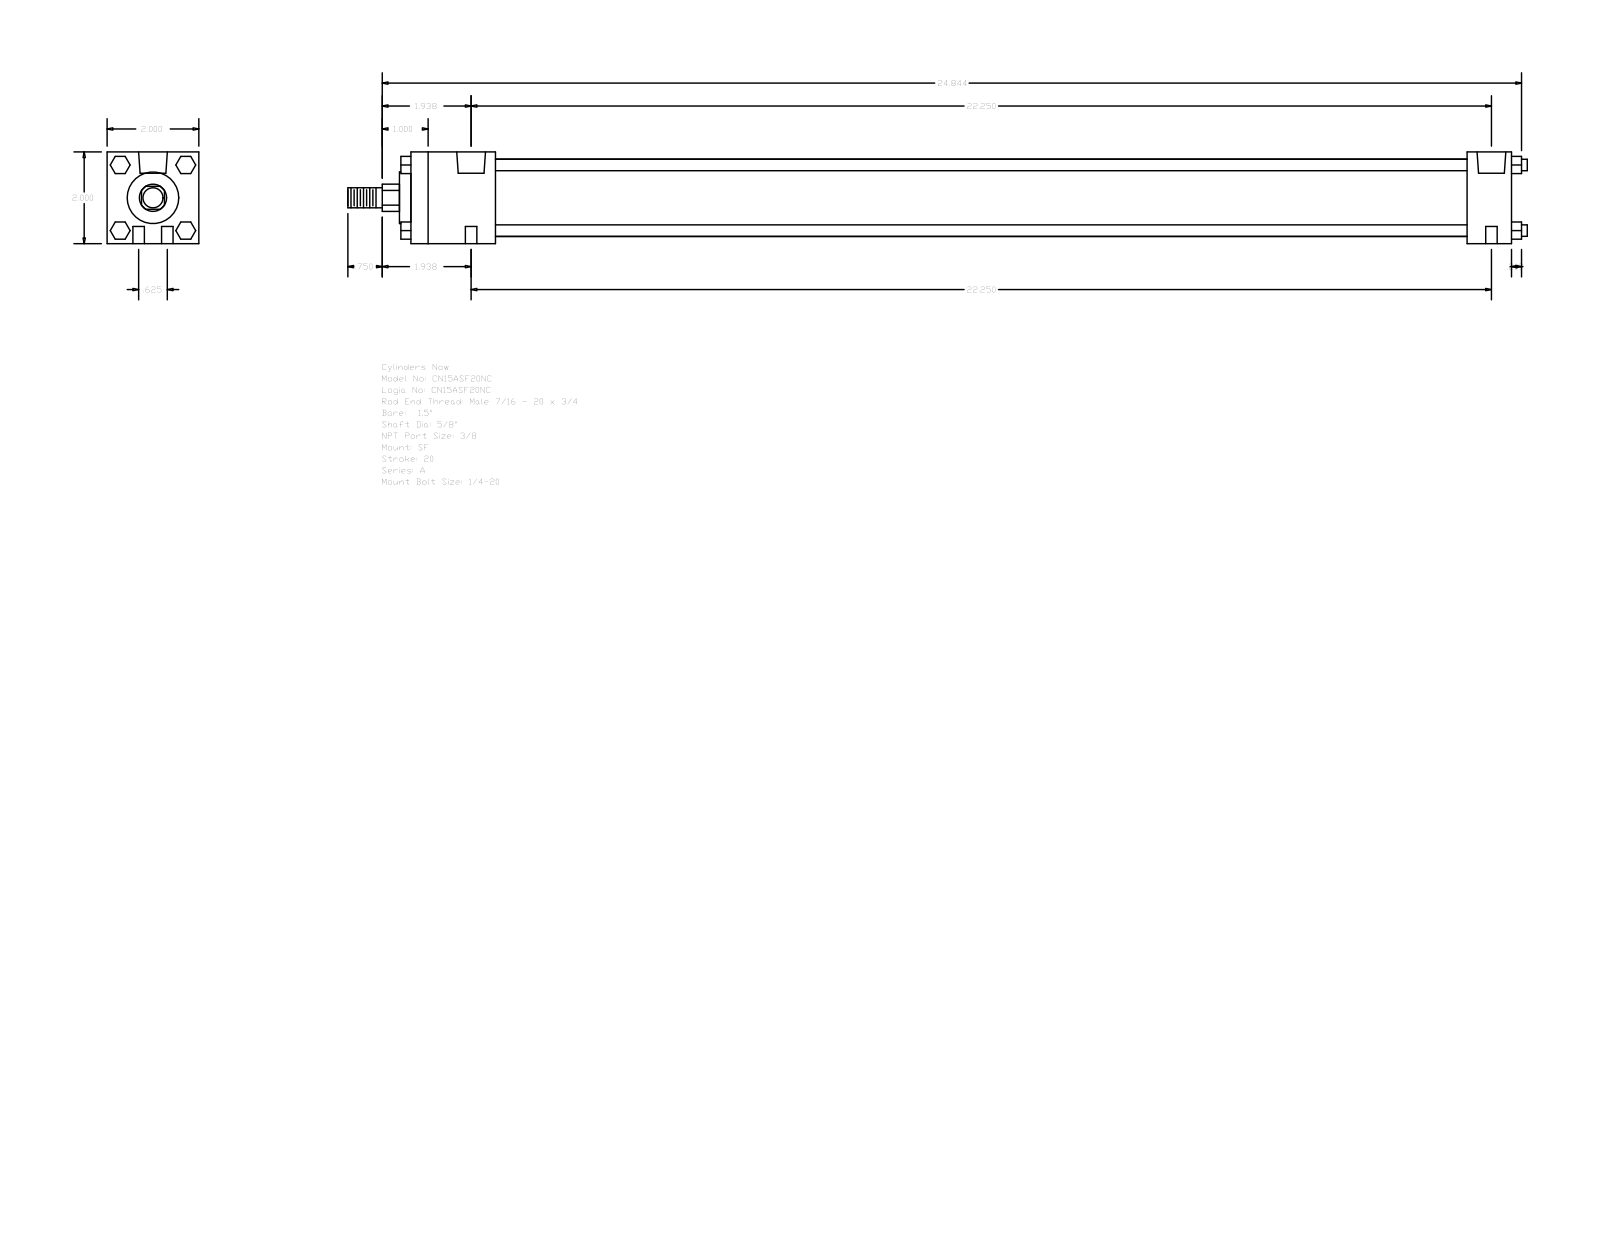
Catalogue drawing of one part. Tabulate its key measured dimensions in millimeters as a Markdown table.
| quantity | value |
| --- | --- |
| part name | A_SF__0150_0.625 |
| STEP written by | GSSL Pune (CONFIG_CONTROL_DESIGN) |
| units | millimeters |
| bodies | 0 solids, 124 faces (94 planar, 30 cylindrical, 0 other) |
| overall size | 653.26 × 50.8 × 50.8 |
| round holes (diameter × count) | 6.35 × 4, 5.56 × 2, 15.93 × 2 |
| round bosses / shafts (diameter × count) | 6.35 × 4, 42.93 × 1, 28.57 × 1, 15.88 × 1, 11.11 × 1 |
| partial cylindrical surfaces (radius × count) | 7.54 × 1 |
| main face-to-face distances | 50.8, 609.6, 46.83, 584.99, 538.16, 562.77, 24.61, 6.35, 9.52, 53.18 |
| hole center spacings | 7.94, 565.21, 565.15, 15.88, 565.37, 557.21 |
